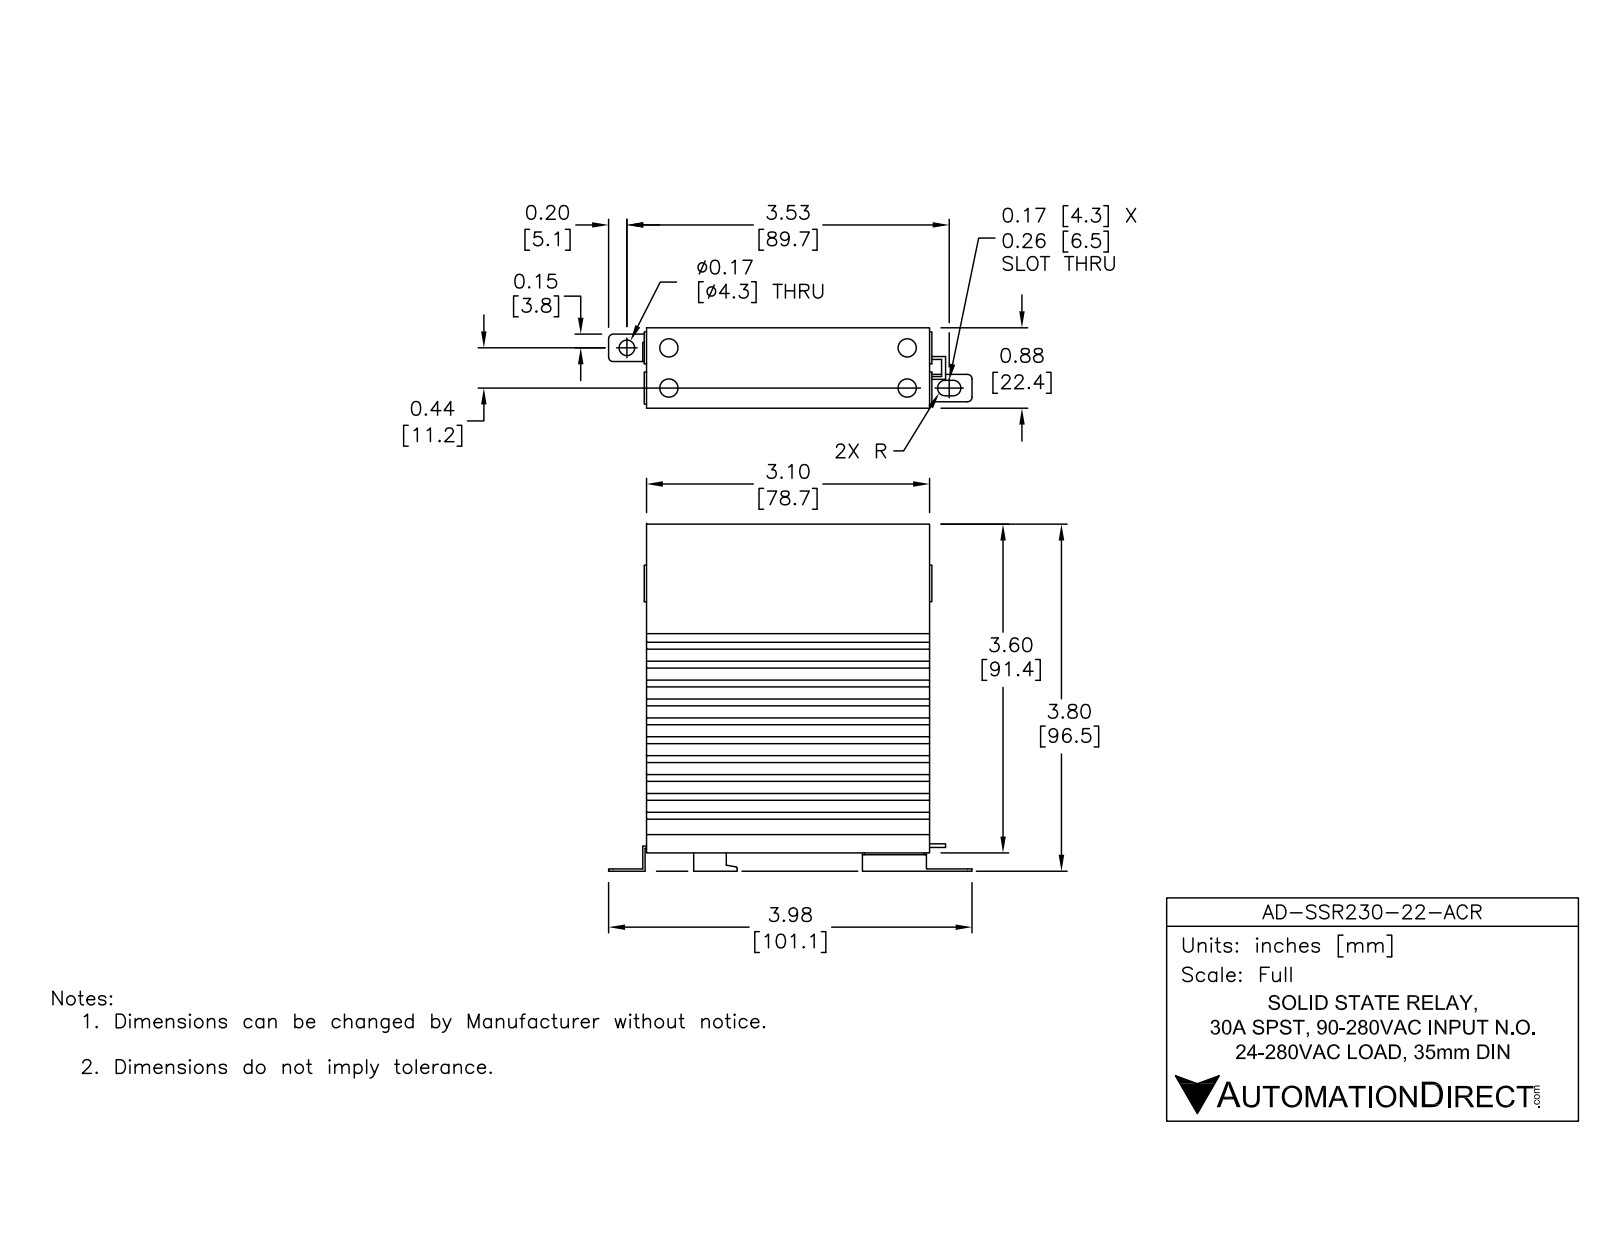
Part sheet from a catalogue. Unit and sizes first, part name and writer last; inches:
Units: inches
Overall size (bounding box): 3.98 × 3.8 × 0.88
Round holes (diameter × count): ⌀0.2 ×4, ⌀0.17 ×1
Partial cylindrical surfaces — rounded edges, fillets, slot ends (radius × count): R0.05 ×6, R0.085 ×2, R0.015 ×1
Main face-to-face distances: 0.62, 0.207, 0.827, 0.414, 0.132, 0.489, 0.339, 0.413, 0.075, 0.207
Hole centre spacings: 0.44, 2.61, 2.647, 0.46, 0.637, 3.07, 3.102
Volume: 7.136 in³ · Surface area: 74.91 in²
Bodies: 1 solid, 215 faces (195 planar, 20 cylindrical, 0 other)
Part name (STEP PRODUCT): AD-SSR230-22-ACR
STEP written by: SolidWorks 2014 (AUTOMOTIVE_DESIGN)
